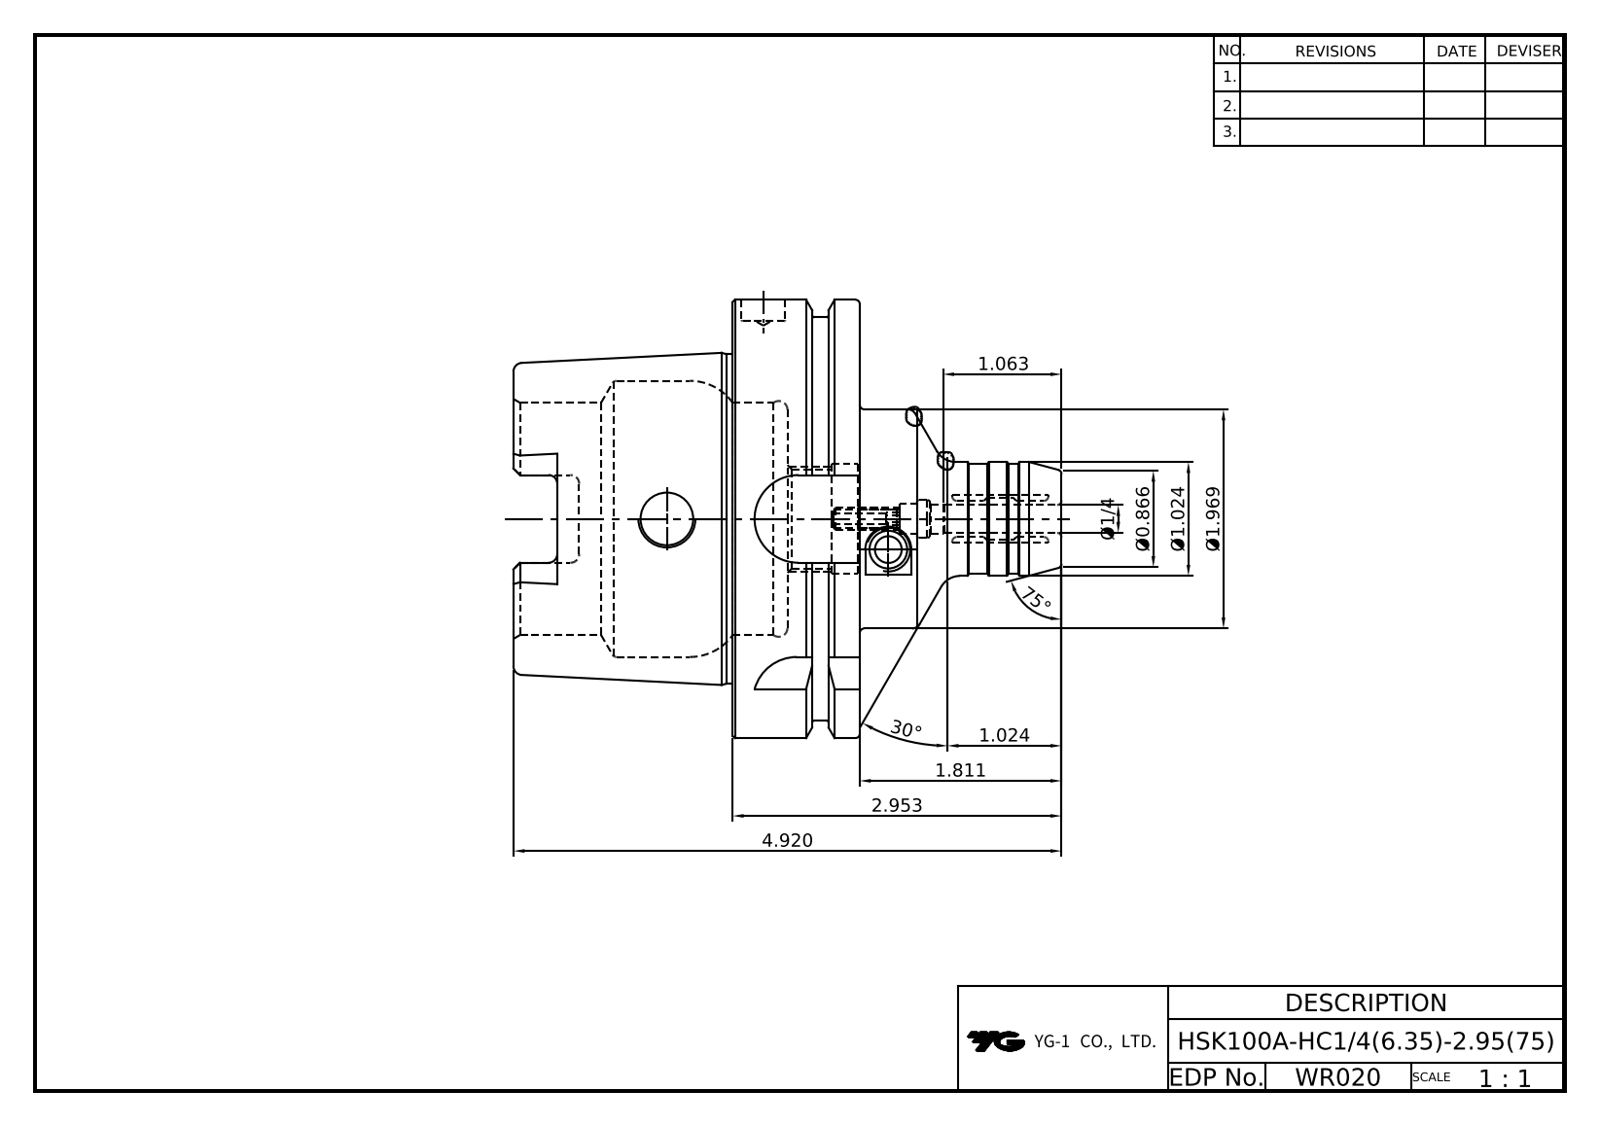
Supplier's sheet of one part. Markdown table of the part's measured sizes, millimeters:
| quantity | value |
| --- | --- |
| part name | LO-HSK100A-HC6.35-75 |
| STEP written by | Autodesk Inventor 2022 (AUTOMOTIVE_DESIGN) |
| units | millimeters |
| bodies | 1 solid, 136 faces (39 planar, 40 cylindrical, 57 other) |
| overall size | 125 × 100 × 100 |
| volume | 299 698 mm³ |
| surface area | 54 652 mm² |
| round holes (diameter × count) | 12 × 2, 4.3 × 1, 6.35 × 1, 6.8 × 1, 10 × 1, 22.38 × 1, 53 × 1, 63 × 1 |
| round bosses / shafts (diameter × count) | 100 × 1, 92 × 1, 75.41 × 1, 50 × 1, 26 × 1, 25 × 1 |
| partial cylindrical surfaces (radius × count) | 2 × 6, 4.88 × 4, 10 × 4 |
| main face-to-face distances | 29, 12.5, 16.5, 62.5, 50, 79, 88, 56.88, 53.12, 28.5 |
